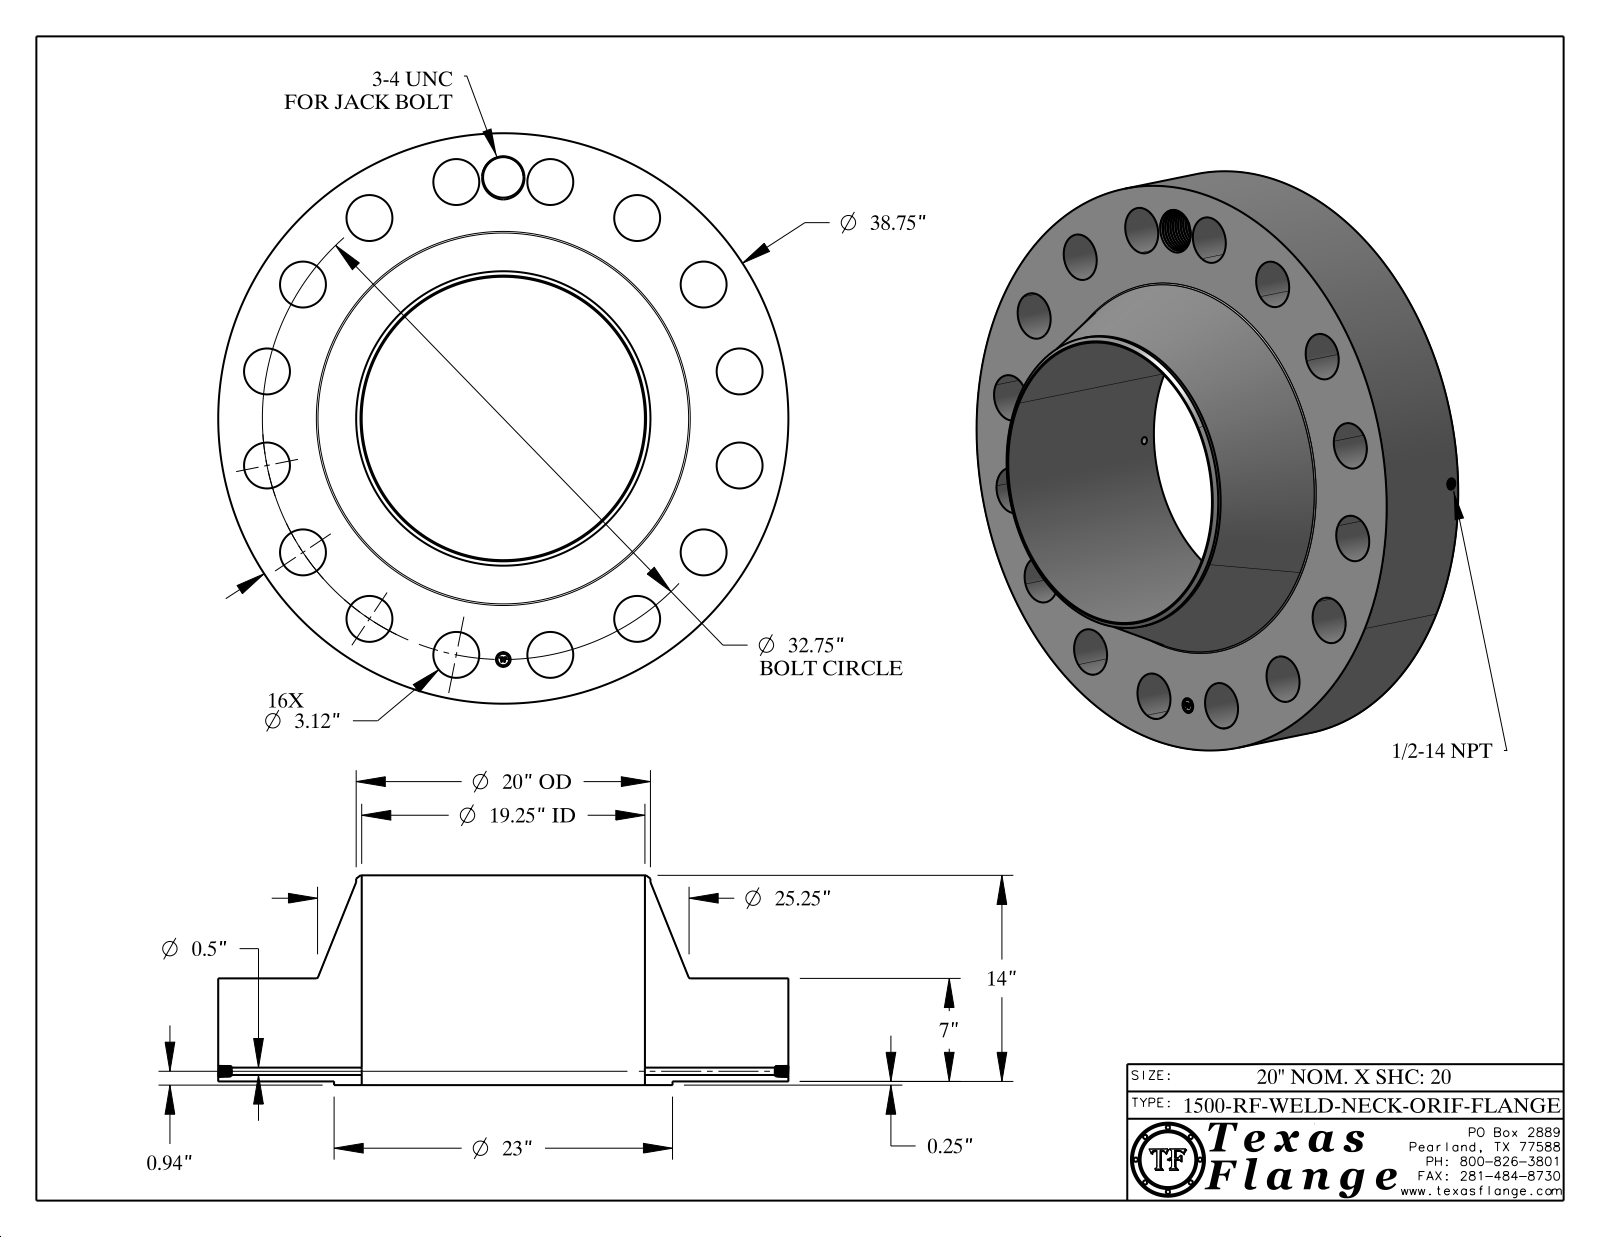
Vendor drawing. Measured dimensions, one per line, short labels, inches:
name: 1500-RF-WELD-NECK
written by: CATIA V5 STEP AP214 (AUTOMOTIVE_DESIGN)
unit: in
bodies: 1 solid, 863 faces (369 planar, 136 cylindrical, 358 other)
size: 38.75 × 38.75 × 14.25
volume: 6 089 in³; area: 4 804 in²
holes: 16× ⌀3.12, 1× ⌀0.5, 1× ⌀0.672, 1× ⌀1, 1× ⌀2.75, 1× ⌀19.25
bosses: 8× ⌀0.061, 1× ⌀38.75, 1× ⌀23, 1× ⌀20, 1× ⌀0.788
face distances: 7, 0.25, 7.25, 14.25, 14, 0.015, 7.235, 6.985, 7.015, 0.298
hole spacings: 30.257, 18.195, 27.231, 32.12, 16.375, 6.389, 6.389, 12.533
